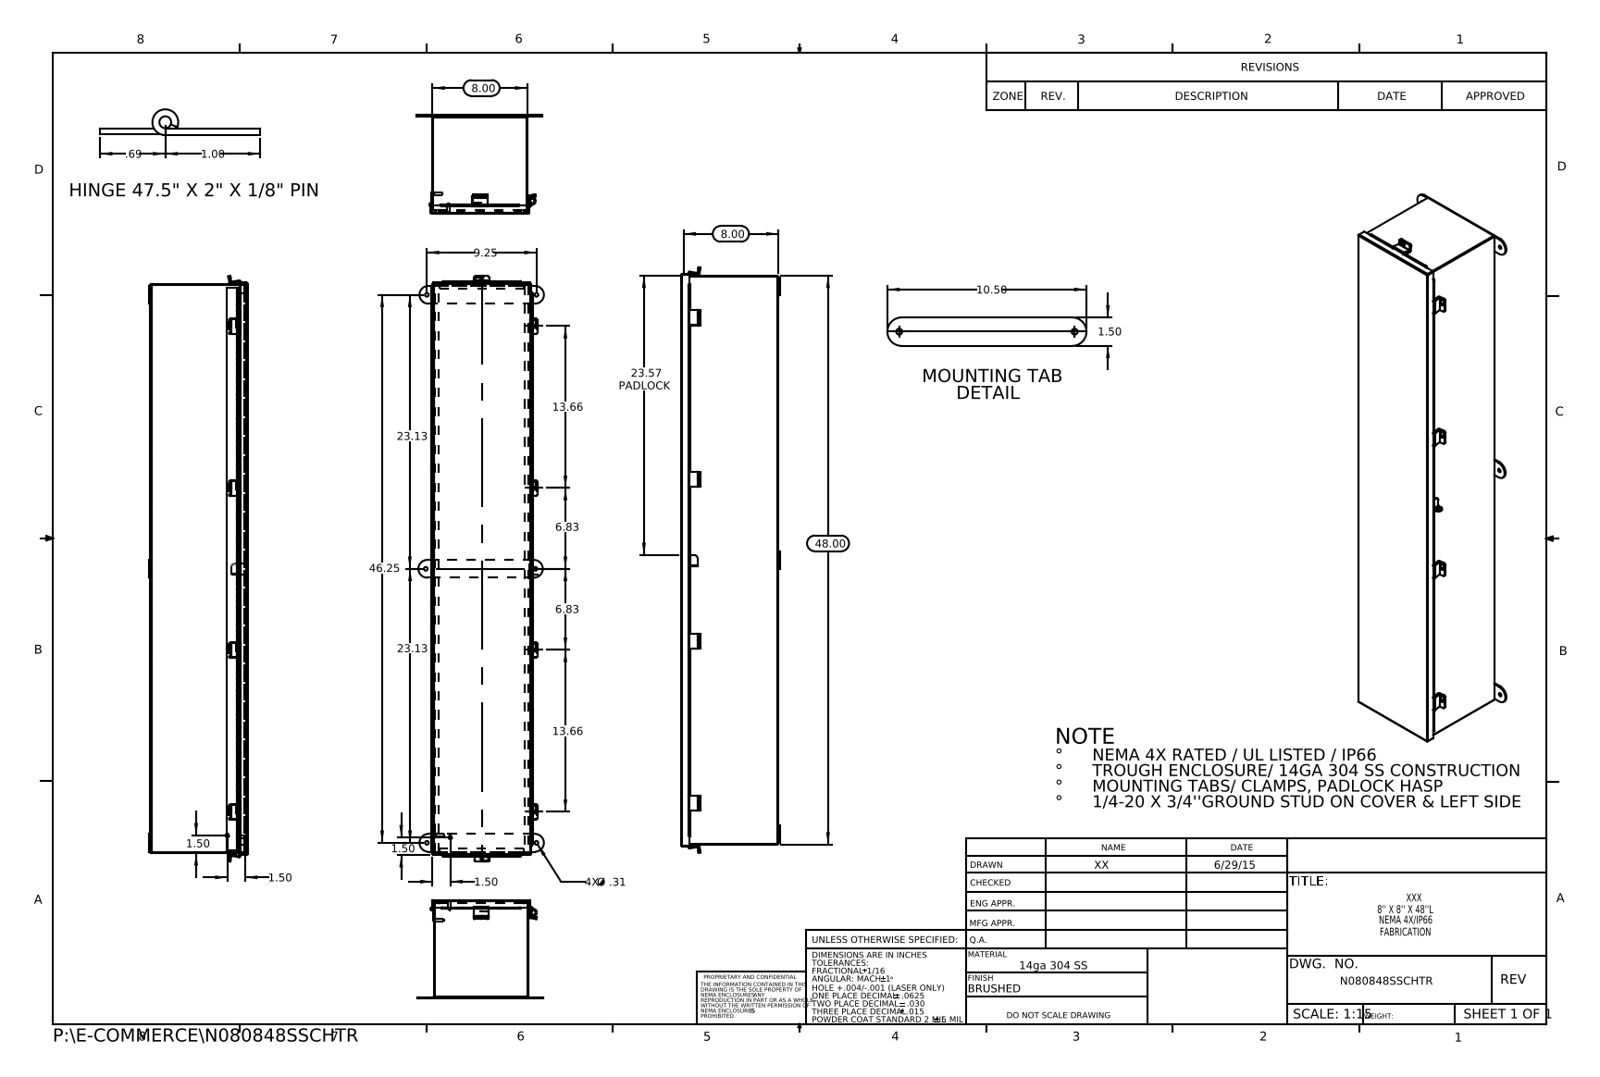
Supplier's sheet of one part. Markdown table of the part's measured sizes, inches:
| quantity | value |
| --- | --- |
| part name | N080848SSCHTR Hinge Body Side; N080848SSCHTR JIC Enclosure Template; N080848SSCHTR JIC Clamp Bracket; N080848SSCHTR HW-CD-S-25020-034 (+8 more) |
| STEP written by | SolidWorks 2015 (CONFIG_CONTROL_DESIGN) |
| units | inches |
| bodies | 24 solids, 1375 faces (821 planar, 534 cylindrical, 20 other) |
| overall size | 49.407 × 10.593 × 8.337 |
| volume | 146.8 in³ |
| surface area | 3 929 in² |
| round holes (diameter × count) | 0.25 × 6, 0.313 × 6, 0.125 × 1, 0.375 × 1 |
| round bosses / shafts (diameter × count) | 0.315 × 2, 0.236 × 2, 0.273 × 1, 0.25 × 1 |
| partial cylindrical surfaces (radius × count) | 0.125 × 23, 0.009 × 12, 0.133 × 12, 0.013 × 11, 0.088 × 11, 0.083 × 6, 0.1 × 6, 0.75 × 6 |
| main face-to-face distances | 0.075, 7.925, 8.128, 8, 7.85, 8.203, 8.053, 0.149, 8.074, 47.925 |
| hole center spacings | 23.125, 9.25, 13.66, 24.872, 24.941, 27.32, 46.25, 47.166 |
